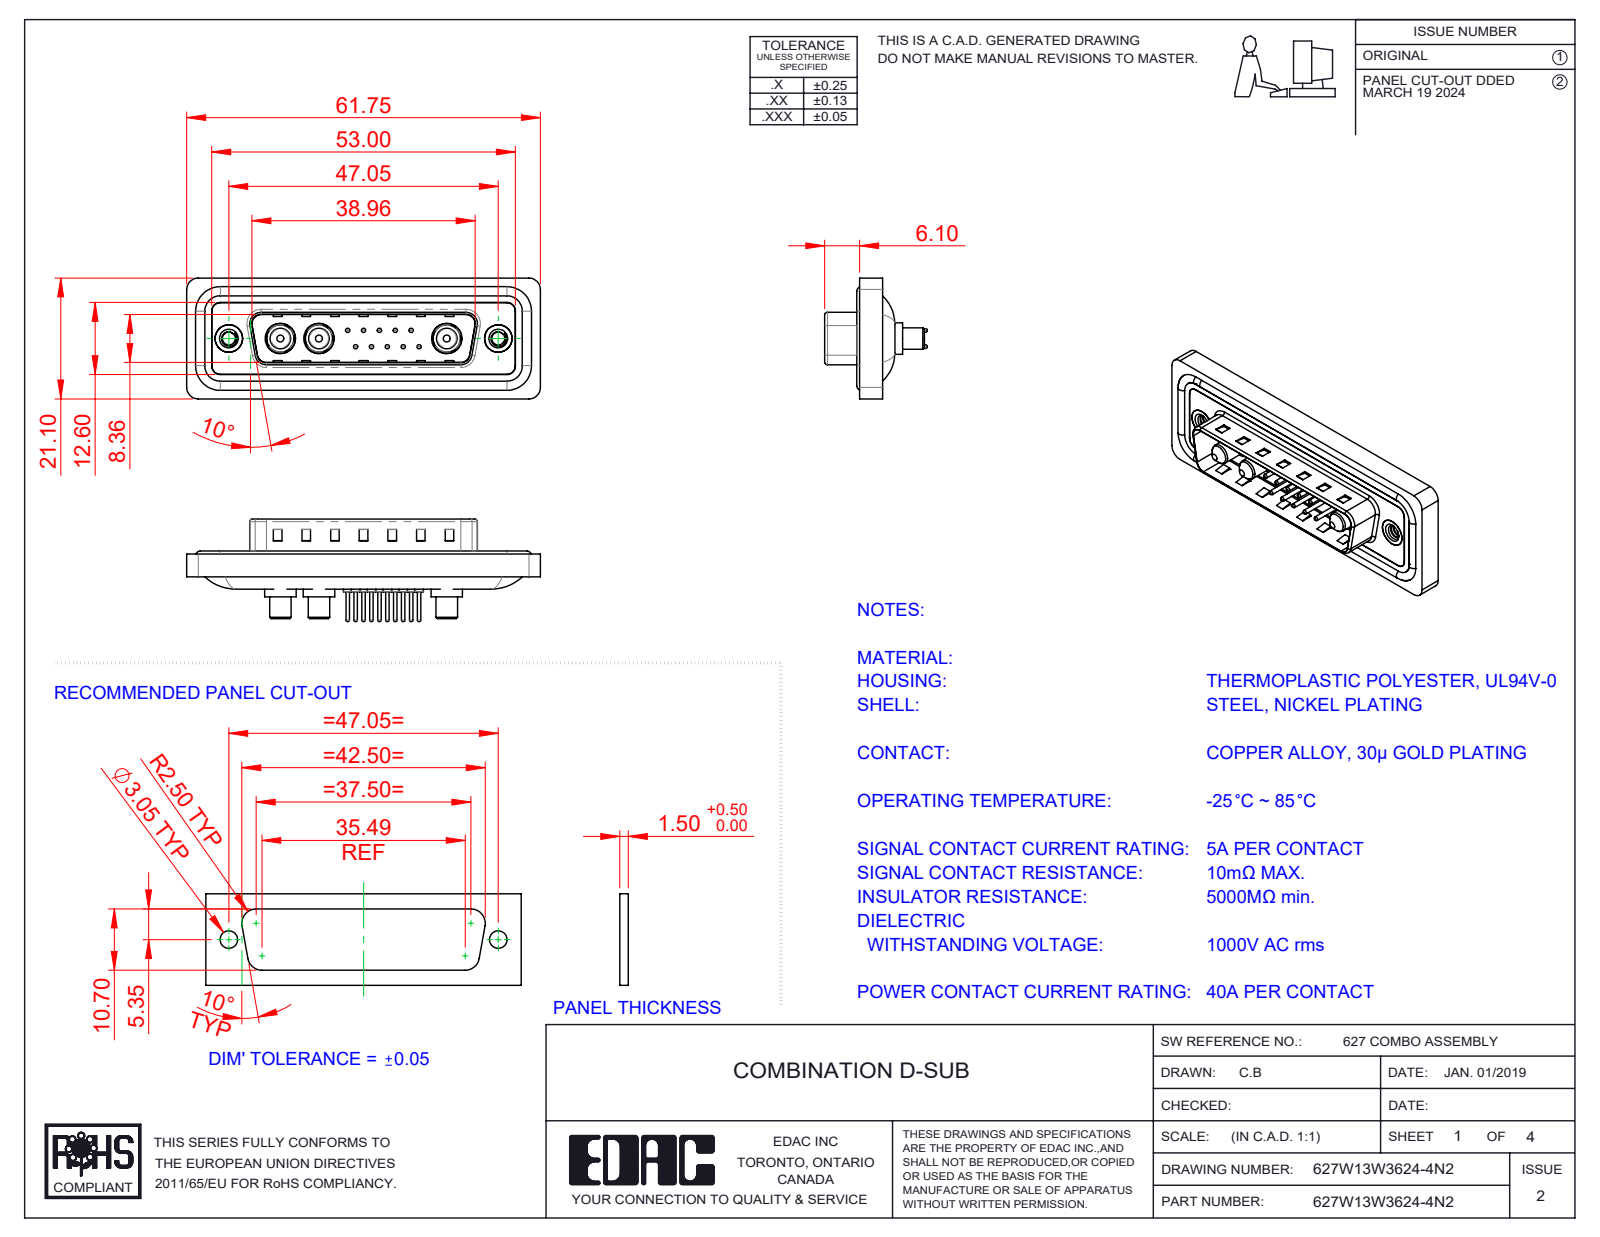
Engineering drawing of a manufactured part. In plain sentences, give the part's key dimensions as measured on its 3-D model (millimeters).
The part is named "627Combo Contact Row 2_24; 627Combo Housing_13W3; 627Combo Shell Rear_25 Contacts; 627Combo Threaded Rivet_2 (+5 more)". Its 3-D file was written by "SolidWorks 2023 (CONFIG_CONTROL_DESIGN)". It is 23 solids with 970 faces: 309 planar, 385 cylindrical and 276 other. Overall it measures 61.75 by 21.1 by 17.9 millimeters. Its volume is 7 391 cubic millimeters and its surface area 11 907 square millimeters. Round holes: 10 of diameter 0.75, 10 of diameter 1.6, 10 of diameter 2, 3 of diameter 4.85, 3 of diameter 5.3, 2 of diameter 2.26, 2 of diameter 4, 2 of diameter 4.8, 2 of diameter 5. Round bosses or shafts: 10 of diameter 1.5, 10 of diameter 0.6, 4 of diameter 1.6, 3 of diameter 5.5, 3 of diameter 5.2, 3 of diameter 4.75, 3 of diameter 3.75, 3 of diameter 3.6. Partial cylindrical surfaces (rounded edges, fillets, slot ends): 22 of radius 1.5, 18 of radius 2, 8 of radius 0.5, 8 of radius 1.6, 4 of radius 0.25, 4 of radius 0.6, 4 of radius 0.65, 4 of radius 0.9. The main face-to-face distances are 0.4, 1.5, 1.1, 1.6, 0.5, 3.1, 2.9, 0.82, 9.58, 4.1. The hole center spacings are 3.16, 2.77, 5.04, 5.54, 7.49, 5.03, 8.31, 10.11.
